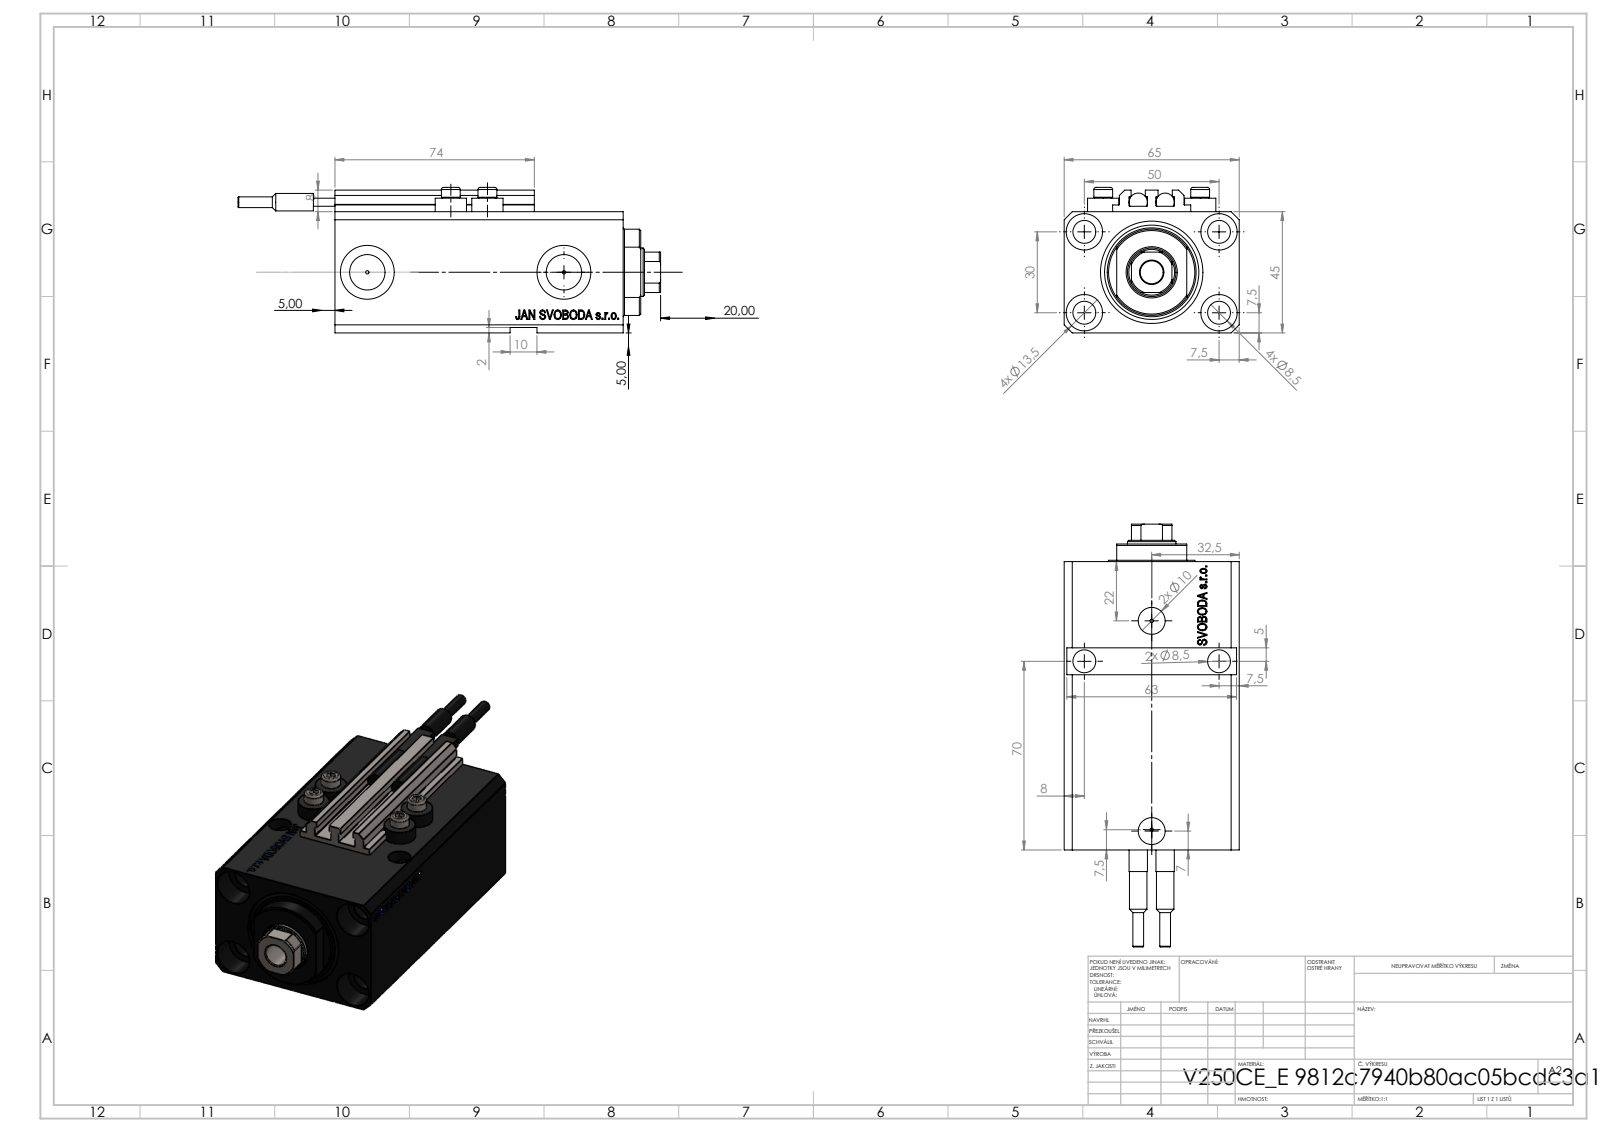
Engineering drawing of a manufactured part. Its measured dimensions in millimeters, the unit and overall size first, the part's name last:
Units: millimetres
Overall size (bounding box): 157 × 65 × 54
Round holes (diameter × count): ⌀8.5 ×9, ⌀1.25 ×4, ⌀4 ×4, ⌀13.5 ×4, ⌀10 ×2, ⌀13.16 ×2, ⌀20 ×2, ⌀18 ×1, ⌀25 ×1, ⌀38 ×1
Round bosses / shafts (diameter × count): ⌀11.6 ×4, ⌀7 ×4, ⌀6.8 ×2, ⌀6.5 ×2, ⌀4 ×2
Partial cylindrical surfaces — rounded edges, fillets, slot ends (radius × count): R0.2 ×10, R8.5 ×1, R16 ×1
Main face-to-face distances: 45, 65, 2, 47, 93, 3, 14, 107, 10, 5
Hole centre spacings: 29.15, 50, 13.6, 14.76, 15.12, 27.51, 27.89, 30
Volume: 276 972 mm³ · Surface area: 79 626 mm²
Bodies: 10 solids, 1139 faces (543 planar, 158 cylindrical, 438 other)
Part name (STEP PRODUCT): ALLEN BOLT V250CE; SWITCH_V250CE; V250CE_VC_E; V250CE_C_VCP (+1 more)
STEP written by: SolidWorks 2019 (CONFIG_CONTROL_DESIGN)
